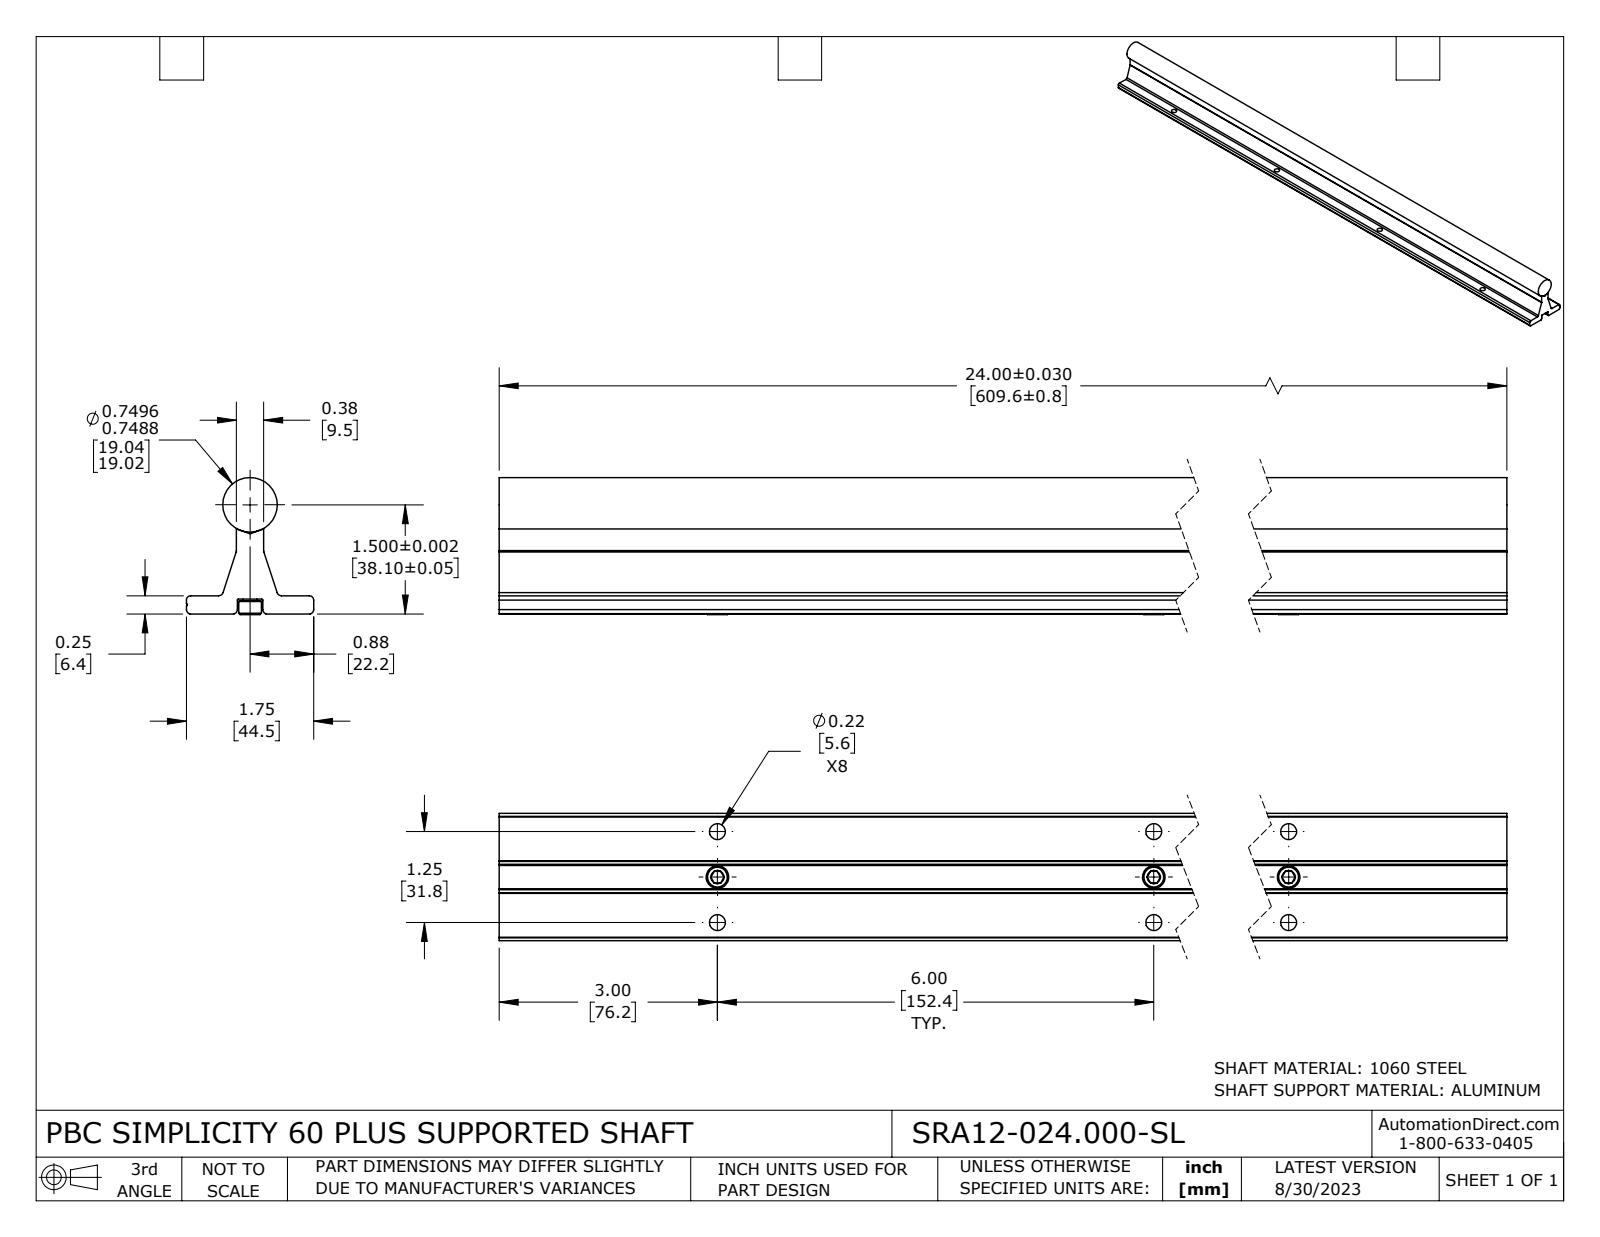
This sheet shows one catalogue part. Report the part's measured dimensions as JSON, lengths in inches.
{"part_name": "SRA12-024.000-SL", "step_written_by": "SolidWorks 2021 (CONFIG_CONTROL_DESIGN)", "units": "inches", "bodies": {"solids": 6, "faces": 201, "planar": 71, "cylindrical": 70, "other": 60}, "overall_size": [24, 1.885, 1.75], "volume_in3": 30.08, "surface_area_in2": 206, "round_holes": [[0.221, 12], [0.169, 4], [0.25, 4]], "round_bosses_or_shafts": [[0.312, 4], [0.19, 4], [0.75, 1]], "partial_cylinders_radius": [[0.06, 6], [0.015, 2], [0.062, 2], [0.063, 2]], "face_to_face_distances": [0.25, 0.205, 0.045, 0.375, 0.012, 0.363, 0.688, 0.7, 1.05, 1.063], "hole_center_spacings": [6.033, 6, 0.625, 12.016, 6.129, 12, 1.25, 12.065]}
